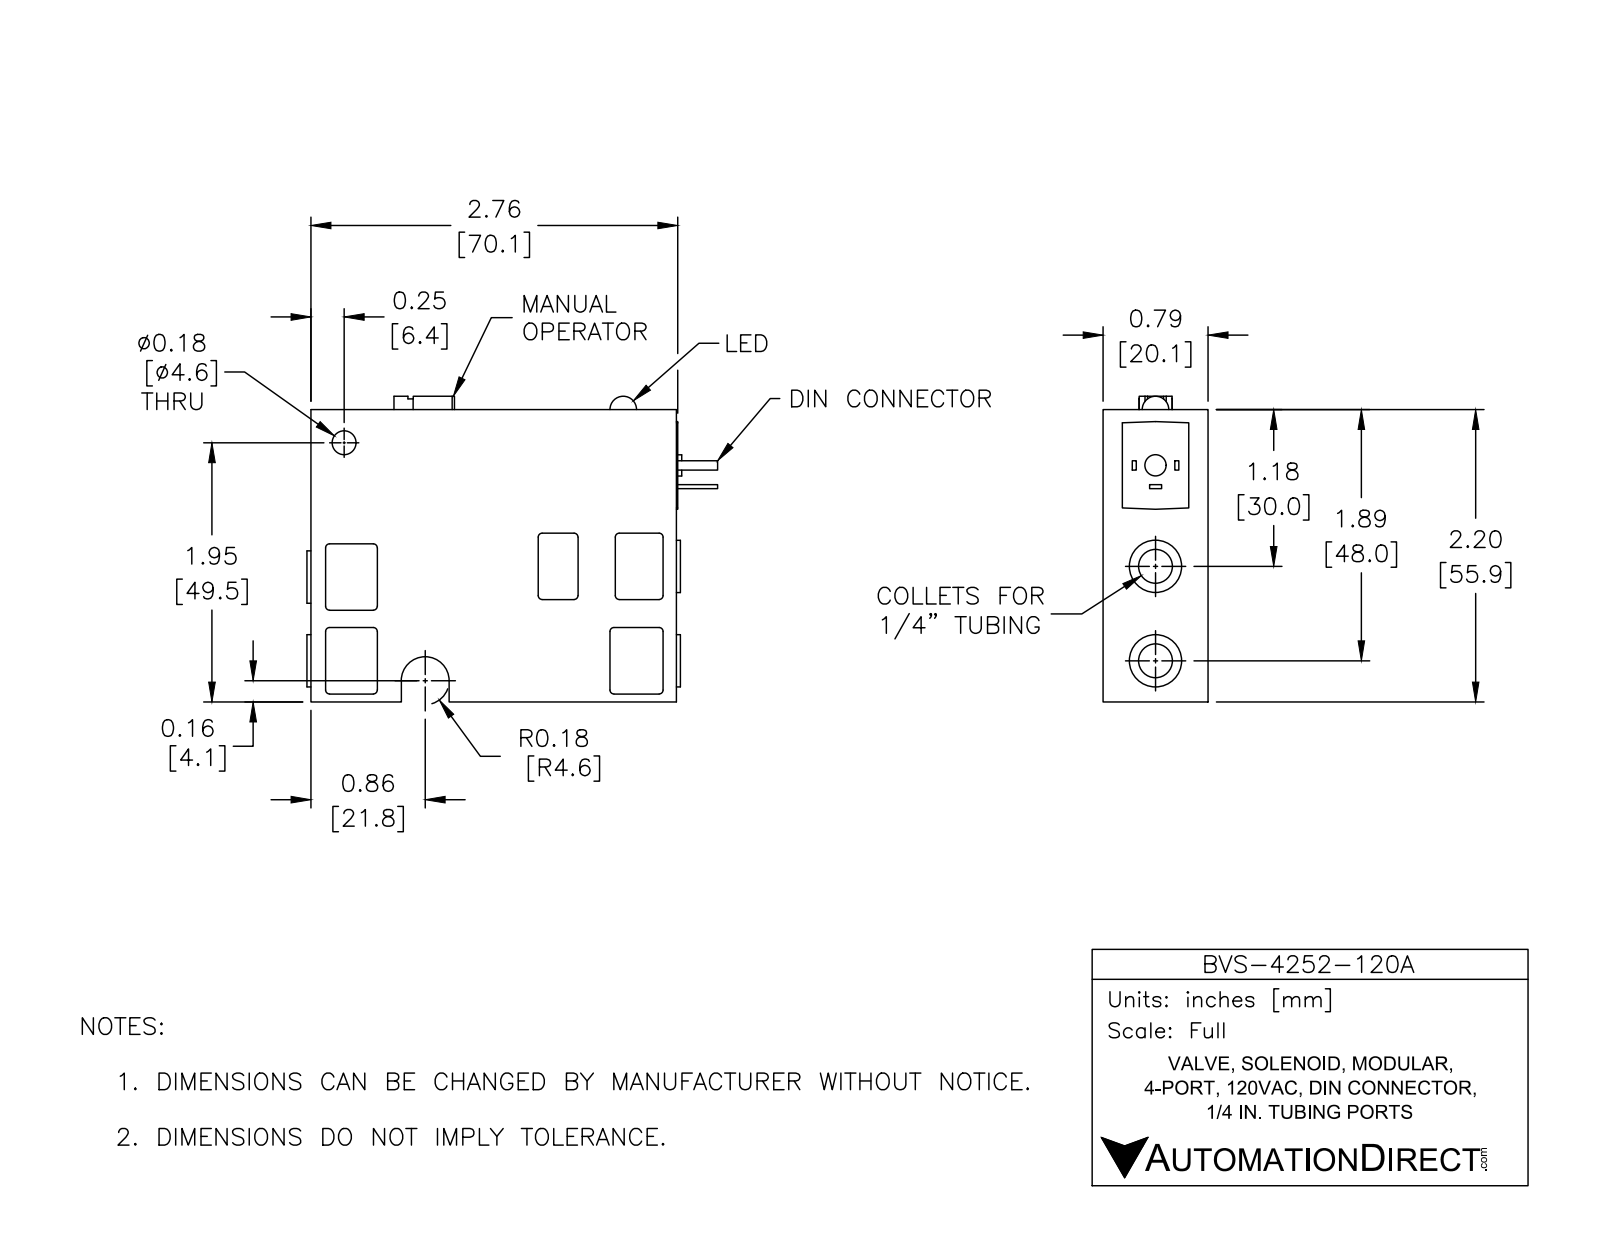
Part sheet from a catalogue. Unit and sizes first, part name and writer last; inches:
Units: inches
Overall size (bounding box): 3.09 × 2.3 × 0.79
Round holes (diameter × count): ⌀0.254 ×3, ⌀0.1 ×1, ⌀0.18 ×1
Round bosses / shafts (diameter × count): ⌀0.394 ×3, ⌀0.16 ×1
Partial cylindrical surfaces — rounded edges, fillets, slot ends (radius × count): R0.03 ×20, R0.02 ×2, R0.125 ×1, R0.18 ×1
Main face-to-face distances: 0.79, 0.1, 2.2, 0.69, 2.75, 0.59, 0.5, 0.11, 2.65, 0.03
Hole centre spacings: 0.08, 0.55, 0.63, 0.63, 0.71, 1.26
Volume: 4.374 in³ · Surface area: 25.19 in²
Bodies: 1 solid, 169 faces (99 planar, 68 cylindrical, 2 other)
Part name (STEP PRODUCT): BVS-4252-120A
STEP written by: SolidWorks 2016 (AUTOMOTIVE_DESIGN)
